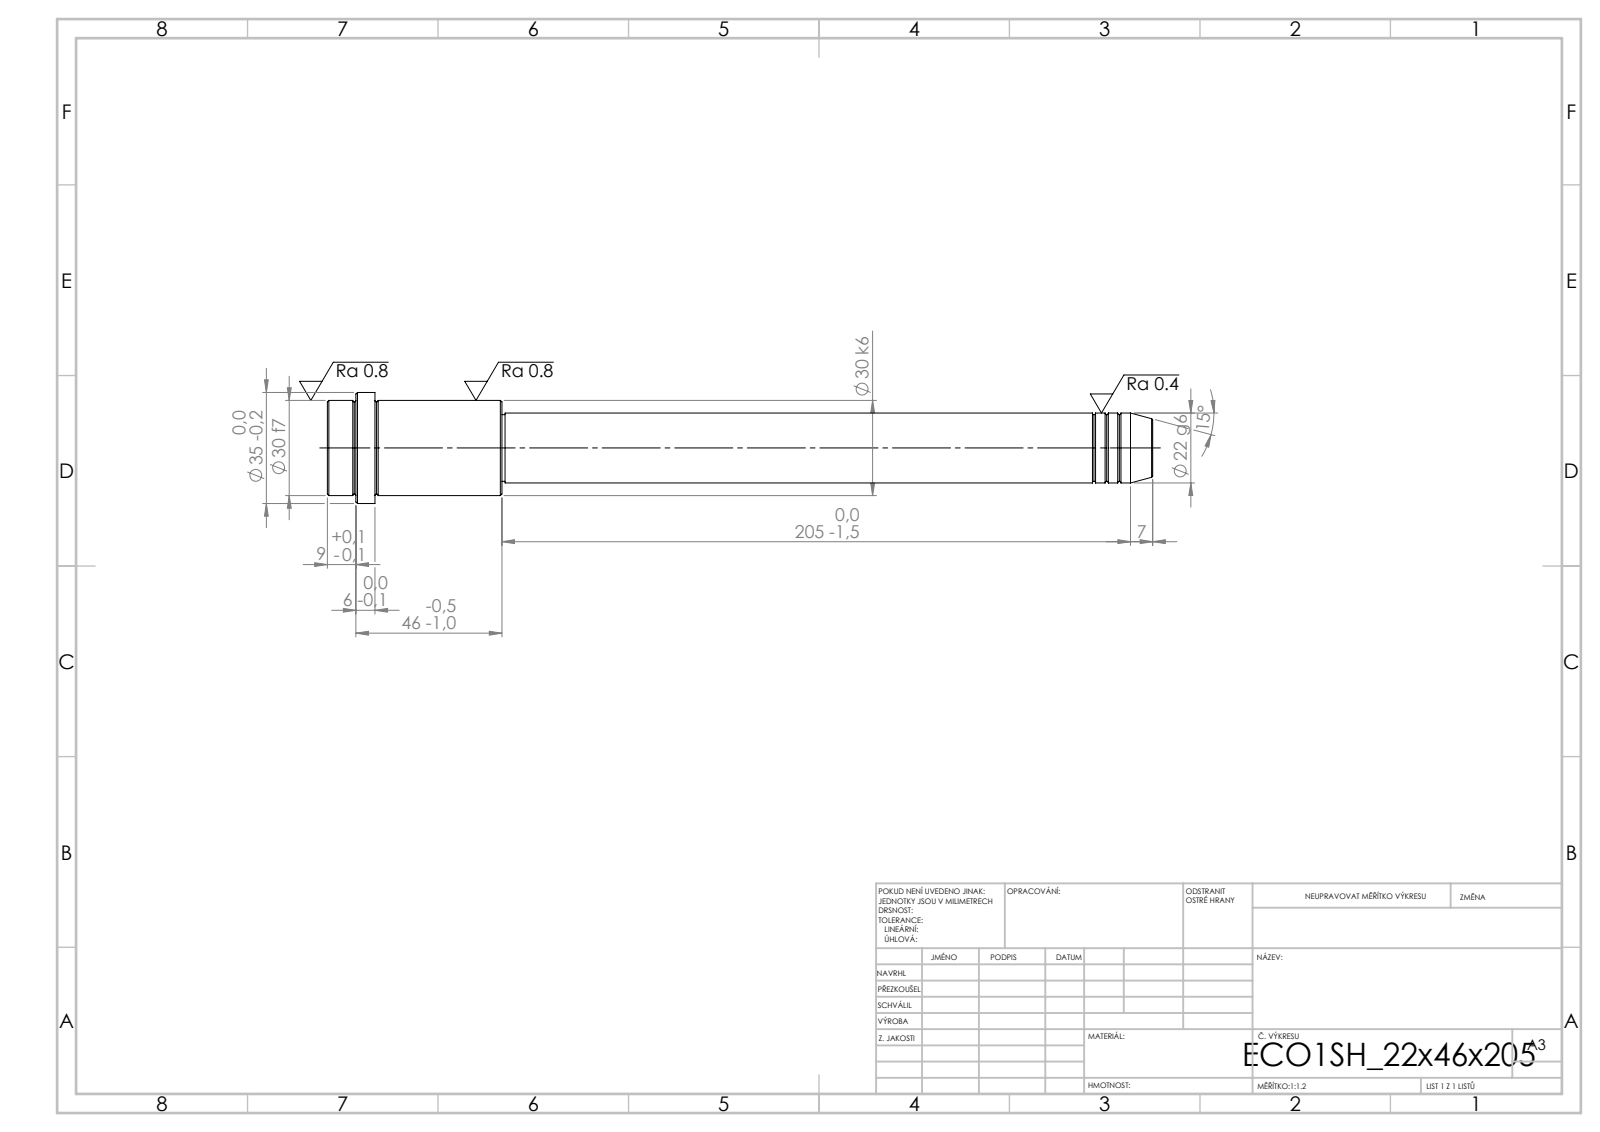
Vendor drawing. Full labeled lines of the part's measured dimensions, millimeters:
STEP written by: SolidWorks 2019 (CONFIG_CONTROL_DESIGN)
Units: millimetres
Bodies: 1 solid, 52 faces (6 planar, 16 cylindrical, 30 other)
Overall size (bounding box): 260 × 35 × 35
Volume: 117 683 mm³ · Surface area: 21 406 mm²
Round bosses / shafts (diameter × count): ⌀35 ×1, ⌀30 ×1, ⌀22 ×1, ⌀21 ×1
Main face-to-face distances: 55, 40, 15, 205, 245, 260, 251, 46, 6, 9
